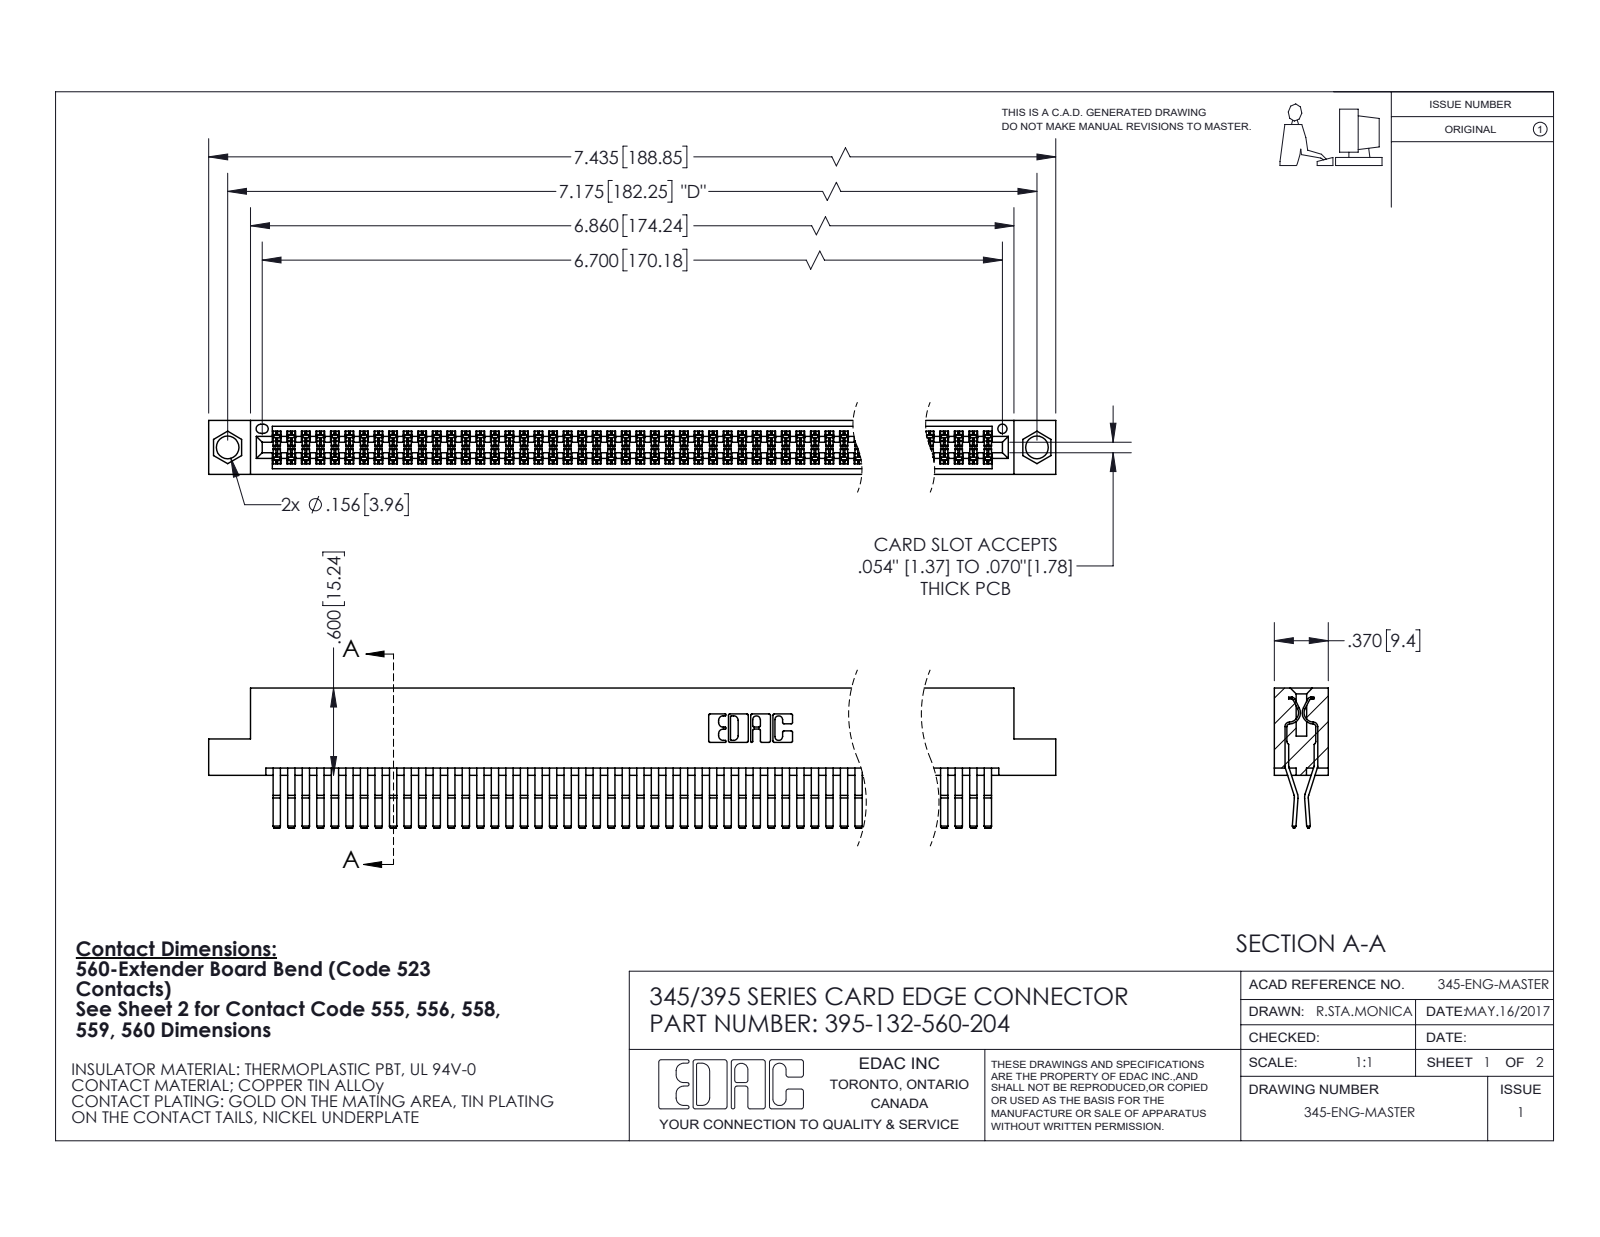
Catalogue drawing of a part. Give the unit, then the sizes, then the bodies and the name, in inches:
Units: inches
Overall size (bounding box): 7.435 × 0.962 × 0.37
Round holes (diameter × count): ⌀0.156 ×2, ⌀0.064 ×1
Partial cylindrical surfaces — rounded edges, fillets, slot ends (radius × count): R0.006 ×198, R0.01 ×22, R0.007 ×6, R0.031 ×6, R0.026 ×3, R0.01 ×2, R0.014 ×2, R0.019 ×2
Main face-to-face distances: 0.025, 0.298, 0.072, 0.37, 0.2, 0.098, 0.272, 0.225, 0.175, 0.149
Hole centre spacings: 0.27, 6.939, 7.175
Volume: 1.179 in³ · Surface area: 48.22 in²
Bodies: 133 solids, 7004 faces (4450 planar, 2554 cylindrical, 0 other)
Part name (STEP PRODUCT): 395-132-560-204; 345-292-001_560 Tail; 345 Part_Flush Mounting Lugs - 0.156 Dia-TI
STEP written by: SolidWorks 2020 (CONFIG_CONTROL_DESIGN)
